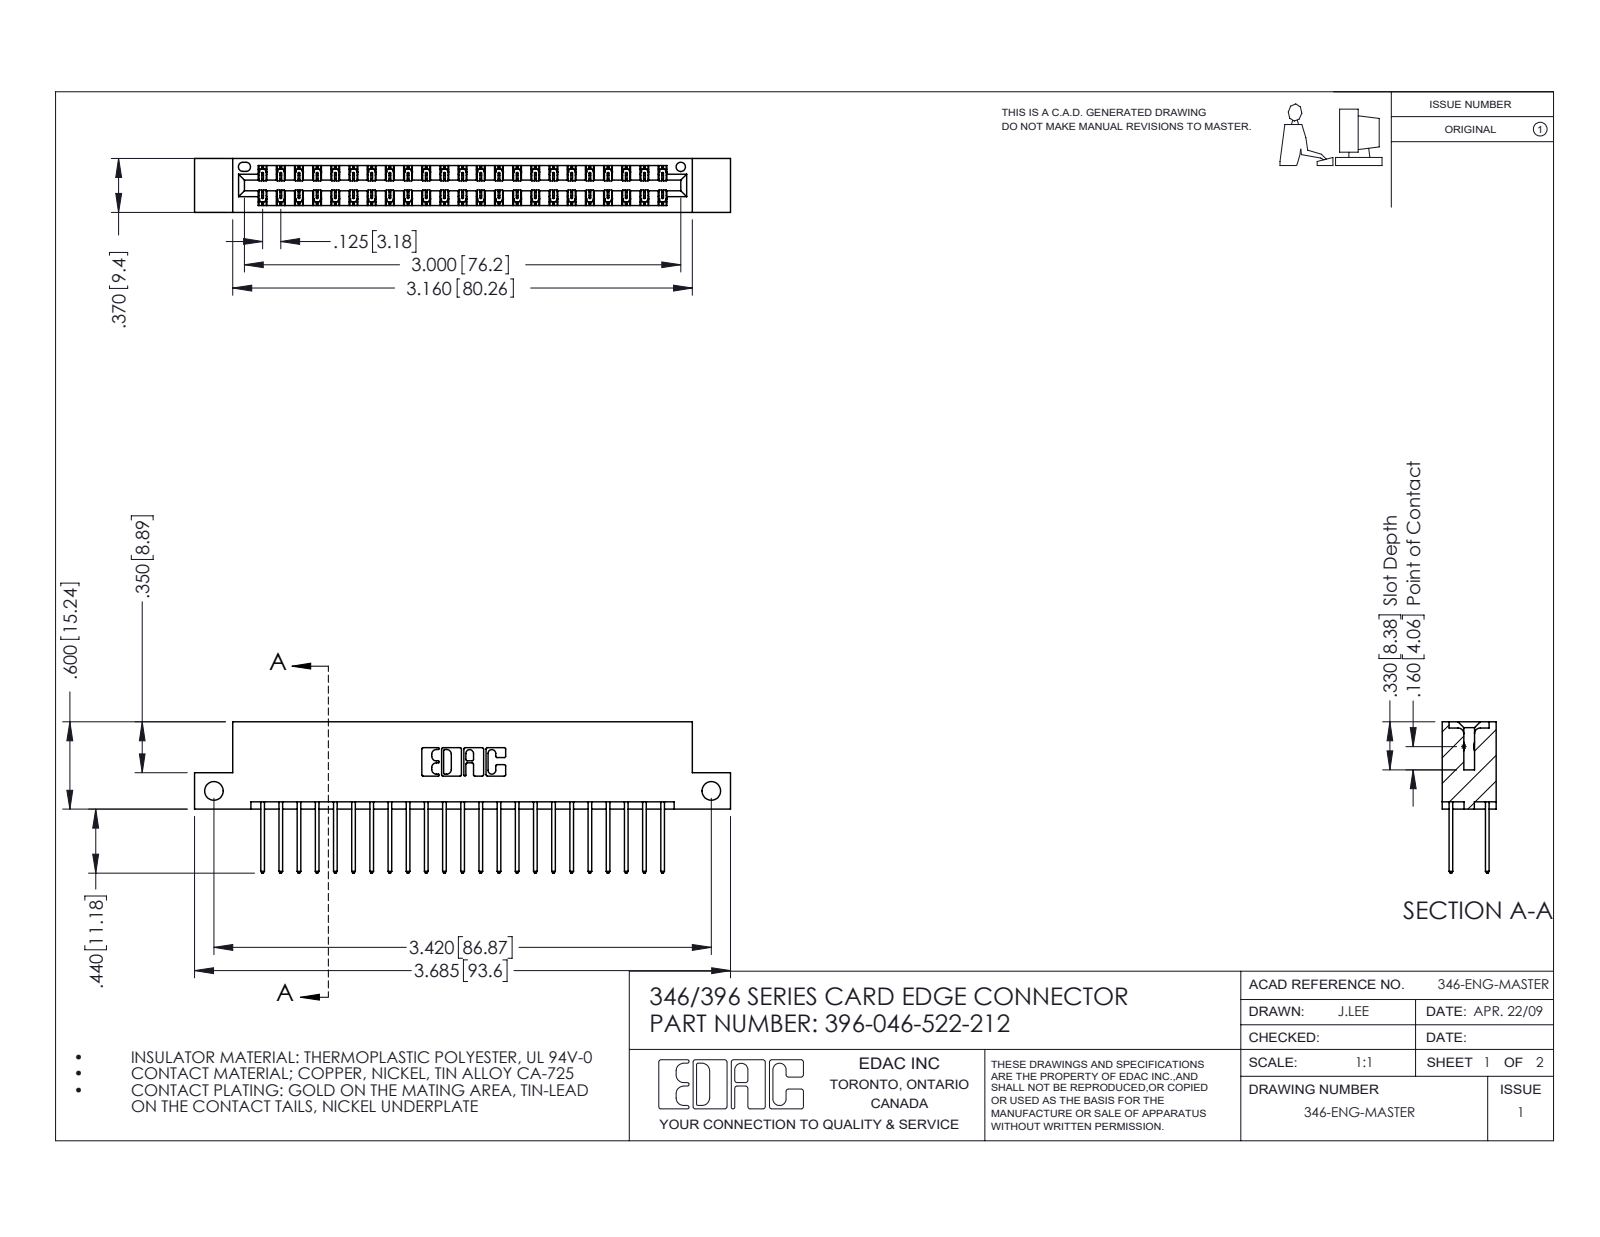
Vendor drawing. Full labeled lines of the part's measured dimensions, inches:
Part name (STEP PRODUCT): 345-292-001_345-293-122; 346 Part_Flush Mounting Lugs - Side Mount; 396-046-522-212
STEP written by: SolidWorks 2016 (CONFIG_CONTROL_DESIGN)
Units: inches
Bodies: 47 solids, 2514 faces (1686 planar, 828 cylindrical, 0 other)
Overall size (bounding box): 3.685 × 1.04 × 0.37
Volume: 0.55 in³ · Surface area: 19.37 in²
Round holes (diameter × count): ⌀0.128 ×2, ⌀0.064 ×1
Partial cylindrical surfaces — rounded edges, fillets, slot ends (radius × count): R0.006 ×69, R0.01 ×46, R0.01 ×22, R0.007 ×6, R0.031 ×6, R0.026 ×3, R0.014 ×2, R0.022 ×2
Main face-to-face distances: 0.048, 0.322, 0.25, 0.37, 0.072, 0.298, 0.025, 0.275, 0.148, 0.222
Hole centre spacings: 3.42
